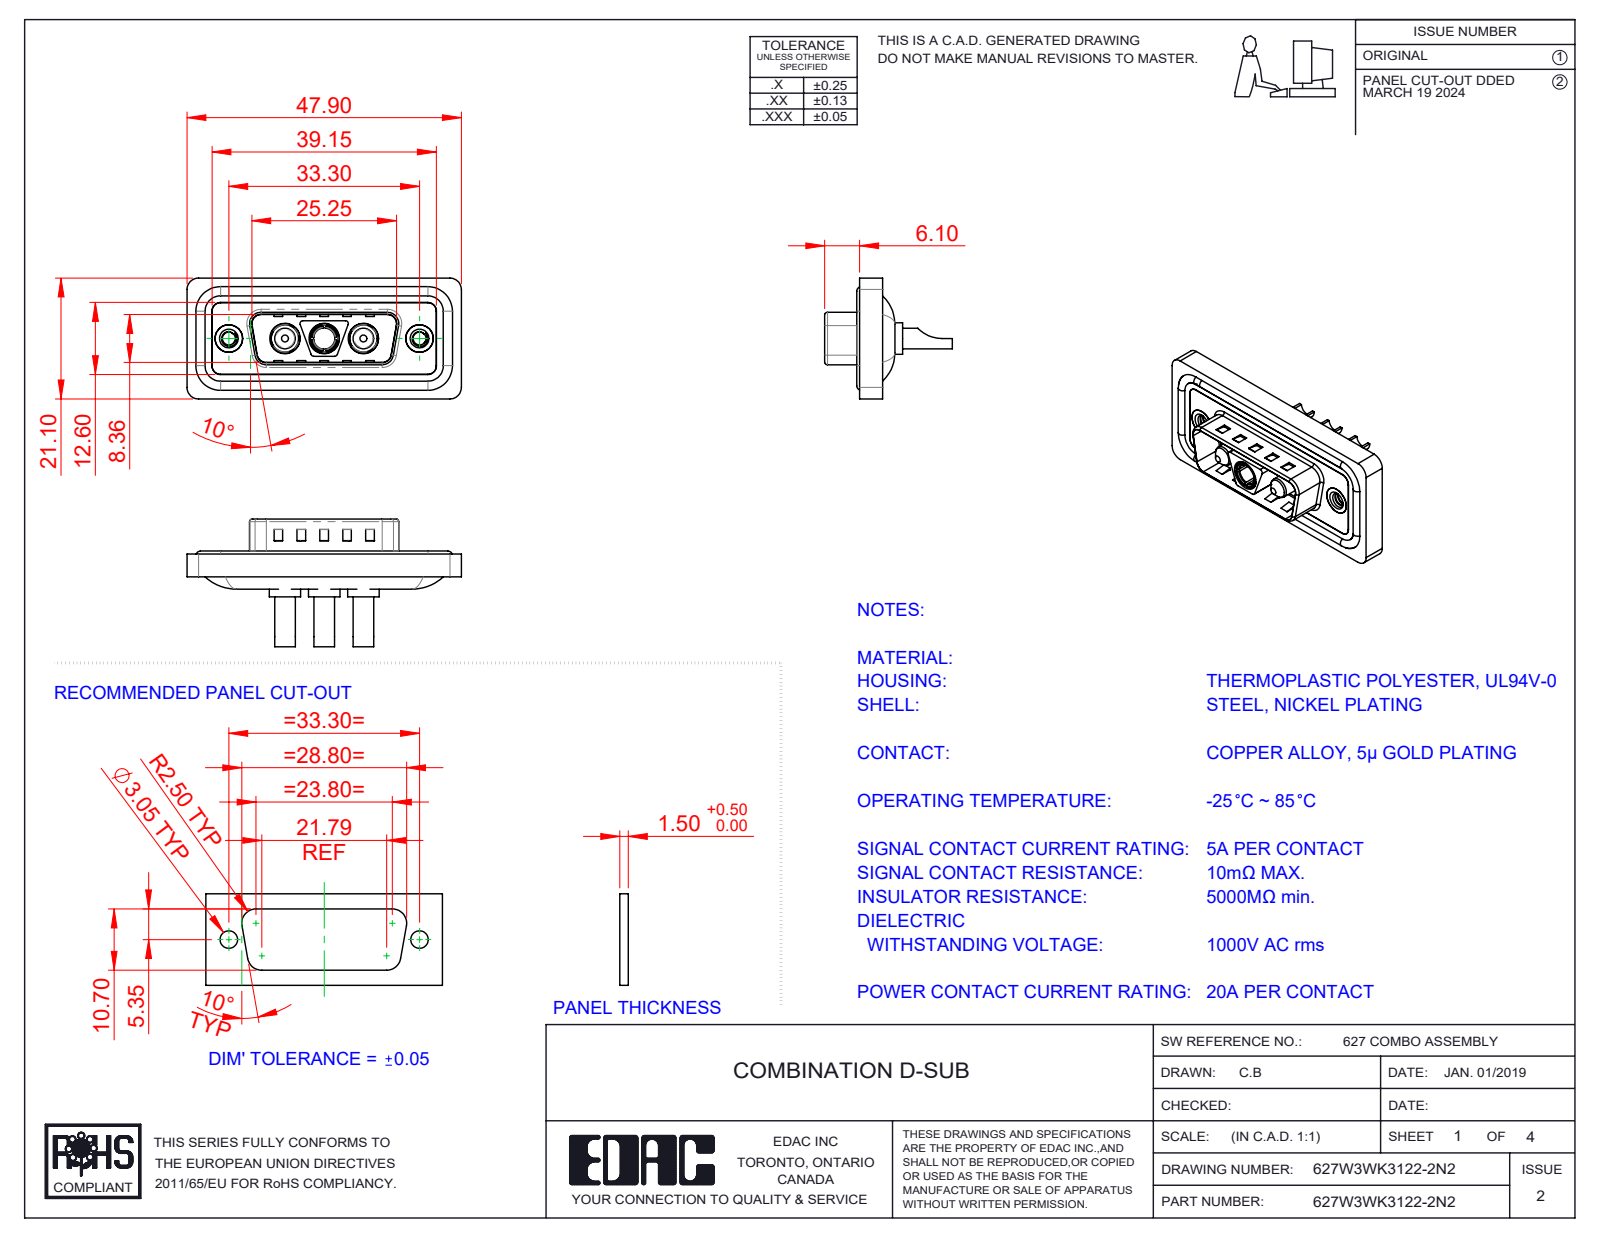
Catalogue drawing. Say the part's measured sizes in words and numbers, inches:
The part is named "627Combo Shell Front_15 Contacts; 627Combo Shell Rear_15 Contacts; 627Combo Threaded Rivet_2; Power Pin_20A SC (+4 more)". Its 3-D file was written by "SolidWorks 2023 (CONFIG_CONTROL_DESIGN)". It is 13 solids with 628 faces: 240 planar, 259 cylindrical and 129 other. Overall it measures 1.886 by 0.878 by 0.831 inches. Its volume is 0.349 cubic inches and its surface area 14.53 square inches. Round holes: 3 of diameter 0.106, 3 of diameter 0.191, 3 of diameter 0.209, 2 of diameter 0.089, 2 of diameter 0.157, 2 of diameter 0.189, 2 of diameter 0.197, 1 of diameter 0.146. Round bosses or shafts: 4 of diameter 0.063, 3 of diameter 0.217, 3 of diameter 0.205, 3 of diameter 0.187, 3 of diameter 0.148, 3 of diameter 0.142, 2 of diameter 0.193, 1 of diameter 0.195. Partial cylindrical surfaces (rounded edges, fillets, slot ends): 26 of radius 0.059, 20 of radius 0.079, 12 of radius 0.02, 8 of radius 0.063, 4 of radius 0.01, 4 of radius 0.024, 4 of radius 0.026, 4 of radius 0.035. The main face-to-face distances are 0.016, 0.043, 0.02, 0.059, 0.063, 0.122, 0.114, 0.157, 0.032, 0.377. The hole center spacings are 0.27, 0.386, 0.656, 0.925, 0.539, 1.311.
